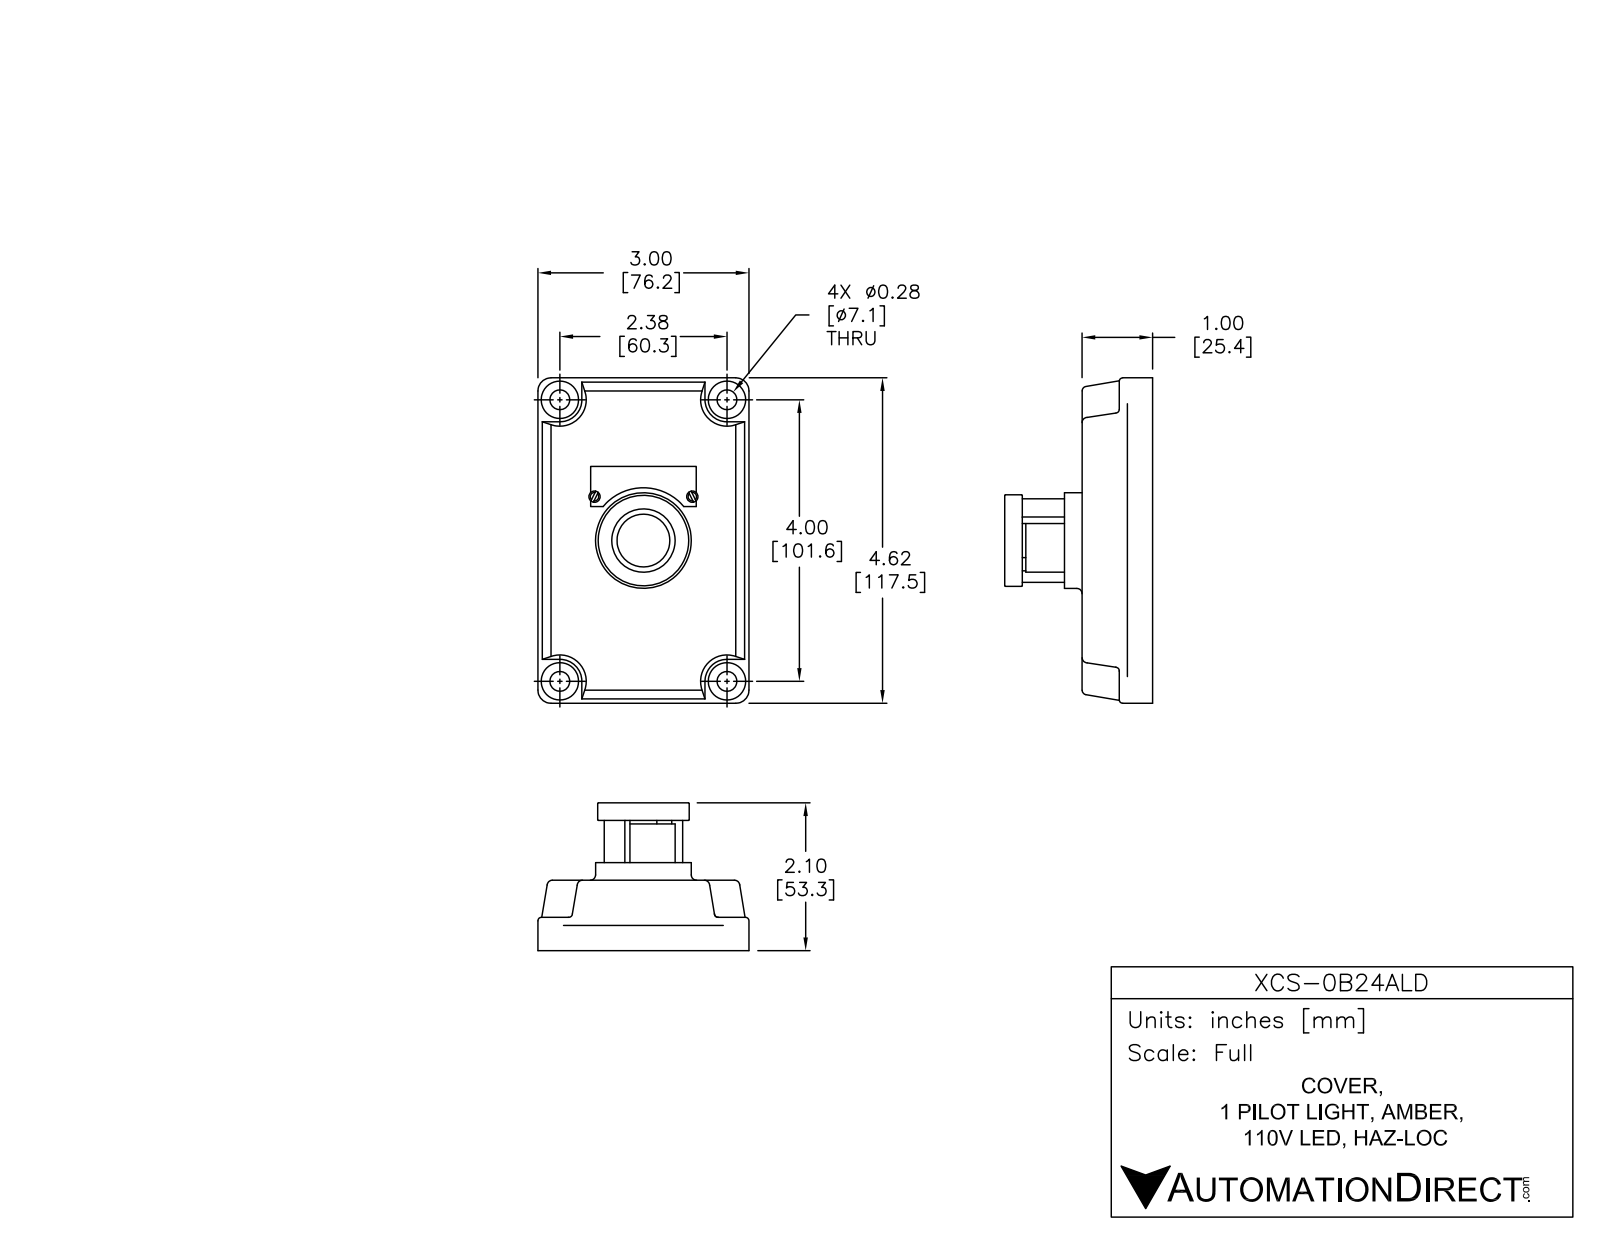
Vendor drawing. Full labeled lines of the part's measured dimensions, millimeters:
Part name (STEP PRODUCT): XCS-0B24ALD
STEP written by: SolidWorks 2015 (AUTOMOTIVE_DESIGN)
Units: millimetres
Bodies: 15 solids, 502 faces (181 planar, 165 cylindrical, 156 other)
Overall size (bounding box): 117.47 × 79.05 × 70.32
Volume: 162 083 mm³ · Surface area: 54 036 mm²
Round holes (diameter × count): ⌀7.24 ×4, ⌀10.25 ×3, ⌀6.3 ×1, ⌀17.5 ×1, ⌀22.61 ×1, ⌀32 ×1, ⌀36.83 ×1
Round bosses / shafts (diameter × count): ⌀4.06 ×6, ⌀11.6 ×4, ⌀6.35 ×4, ⌀31.75 ×1, ⌀22.86 ×1, ⌀15.25 ×1, ⌀10 ×1
Partial cylindrical surfaces — rounded edges, fillets, slot ends (radius × count): R1.5 ×12, R2 ×12, R0.76 ×8, R3 ×8, R6.35 ×8, R1.4 ×6, R1.52 ×6, R0.51 ×4
Main face-to-face distances: 13.34, 12.66, 26, 1.5, 10.13, 22.79, 36.13, 11.63, 24.29, 37.63
Hole centre spacings: 58.92, 24, 40.11, 40.12, 80.53, 80.54, 101.6, 117.84
